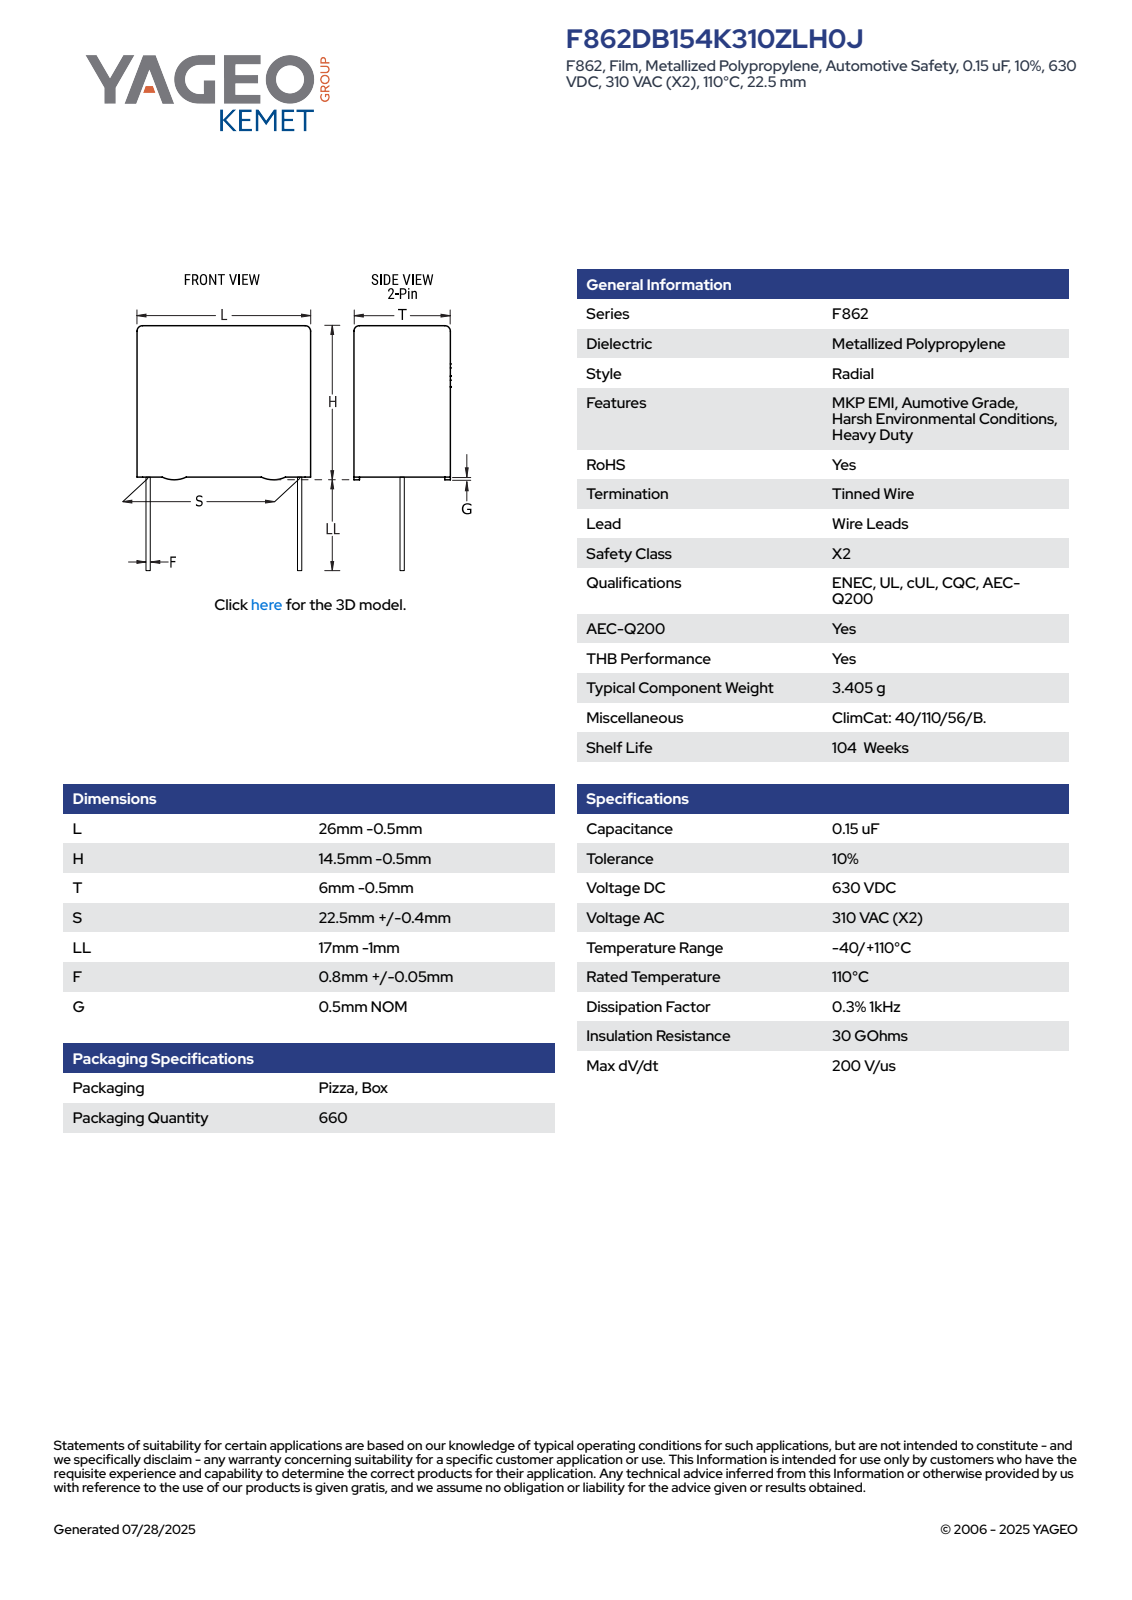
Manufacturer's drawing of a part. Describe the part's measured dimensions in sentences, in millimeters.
The part is named "CFR_RBG_26X14.5X6_L25.5H14T5.5S22.5LL16F0.85G0.5". Its 3-D file was written by "SolidWorks 2014 (AUTOMOTIVE_DESIGN)". It is 4 solids with 89 faces: 81 planar, 8 cylindrical and 0 other. Overall it measures 30 by 25.5 by 5.5 millimeters. Its volume is 1 912 cubic millimeters and its surface area 1 280 square millimeters. Round bosses or shafts: 2 of diameter 0.85. Partial cylindrical surfaces (rounded edges, fillets, slot ends): 4 of radius 0.5. The main face-to-face distances are 5.5, 13.5, 25.5, 0.31, 5.19, 0.5, 14, 4.88, 16, 16.5.
